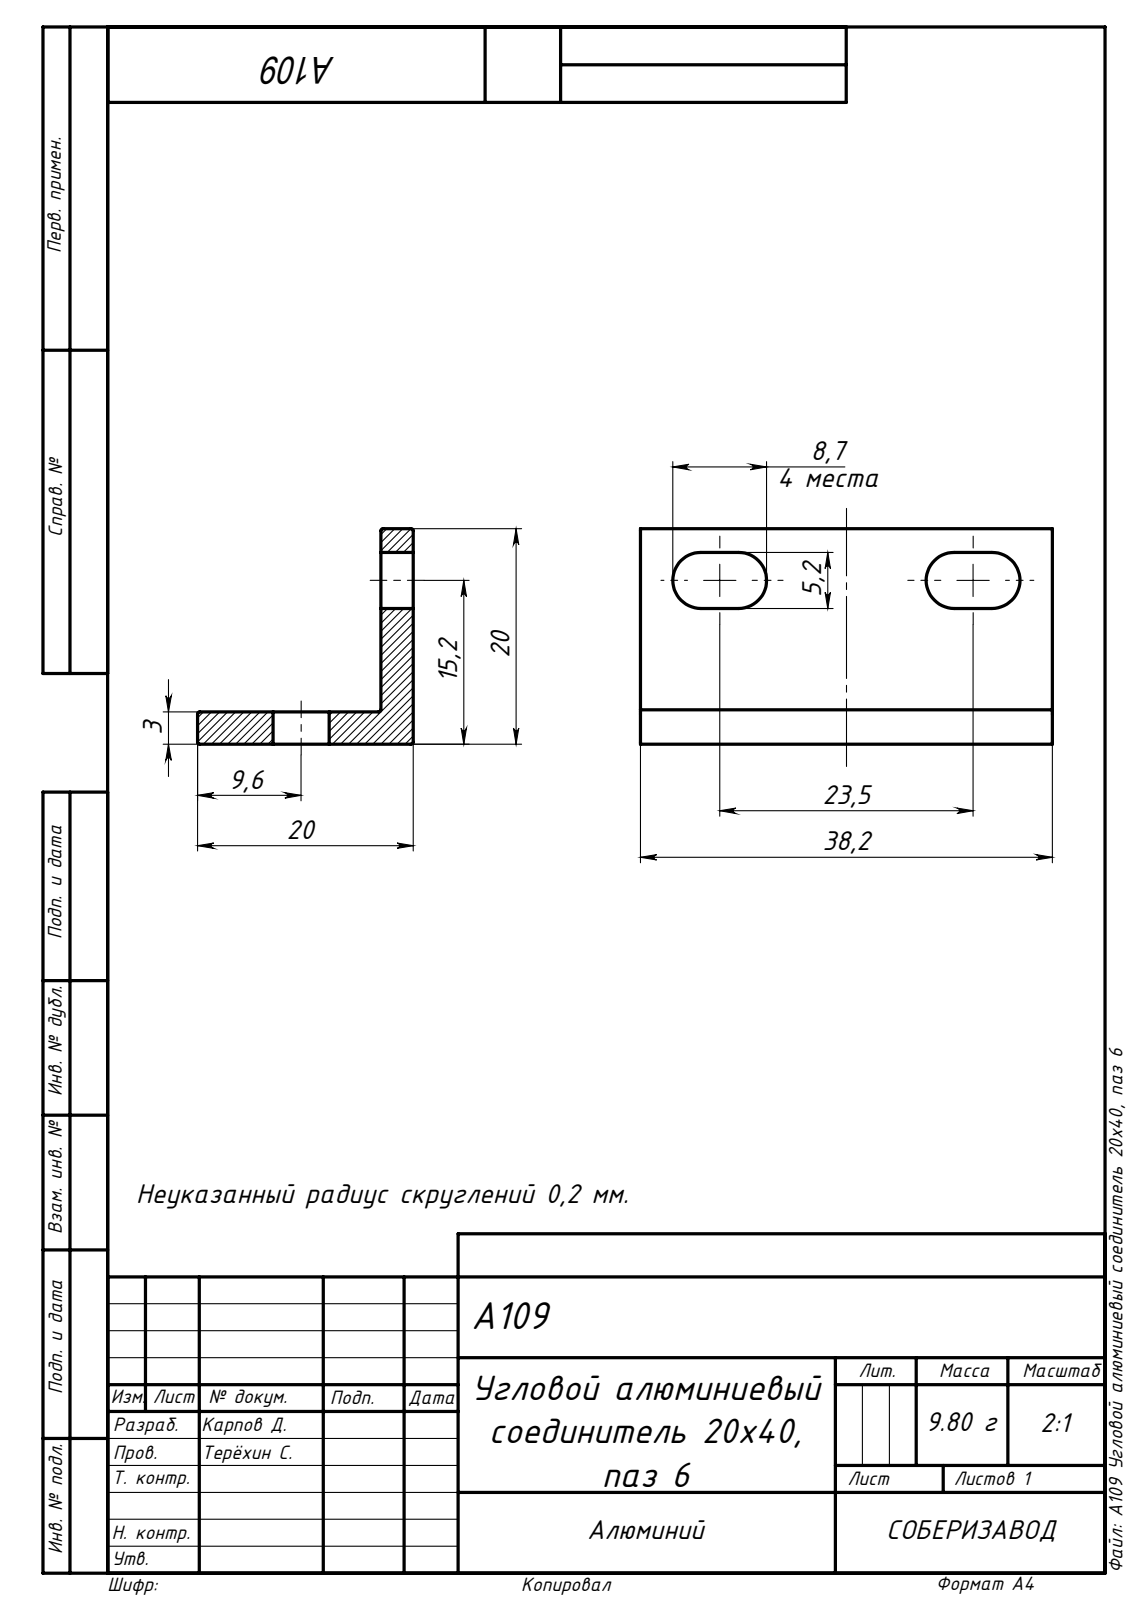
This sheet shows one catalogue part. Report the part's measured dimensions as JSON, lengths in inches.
{"part_name": "A109 Угловой алюминиевый соединитель 20х40, паз 6", "step_written_by": "SolidWorks 2021 (AUTOMOTIVE_DESIGN)", "units": "inches", "bodies": {"solids": 1, "faces": 32, "planar": 16, "cylindrical": 16, "other": 0}, "overall_size": [1.504, 0.787, 0.787], "volume_in3": 0.23, "surface_area_in2": 4.996, "partial_cylinders_radius": [[0.102, 8], [0.008, 6]], "face_to_face_distances": [0.118, 0.787, 0.669, 1.504, 0.205, 0.512, 0.394, 0.276, 0.307, 0.189]}
